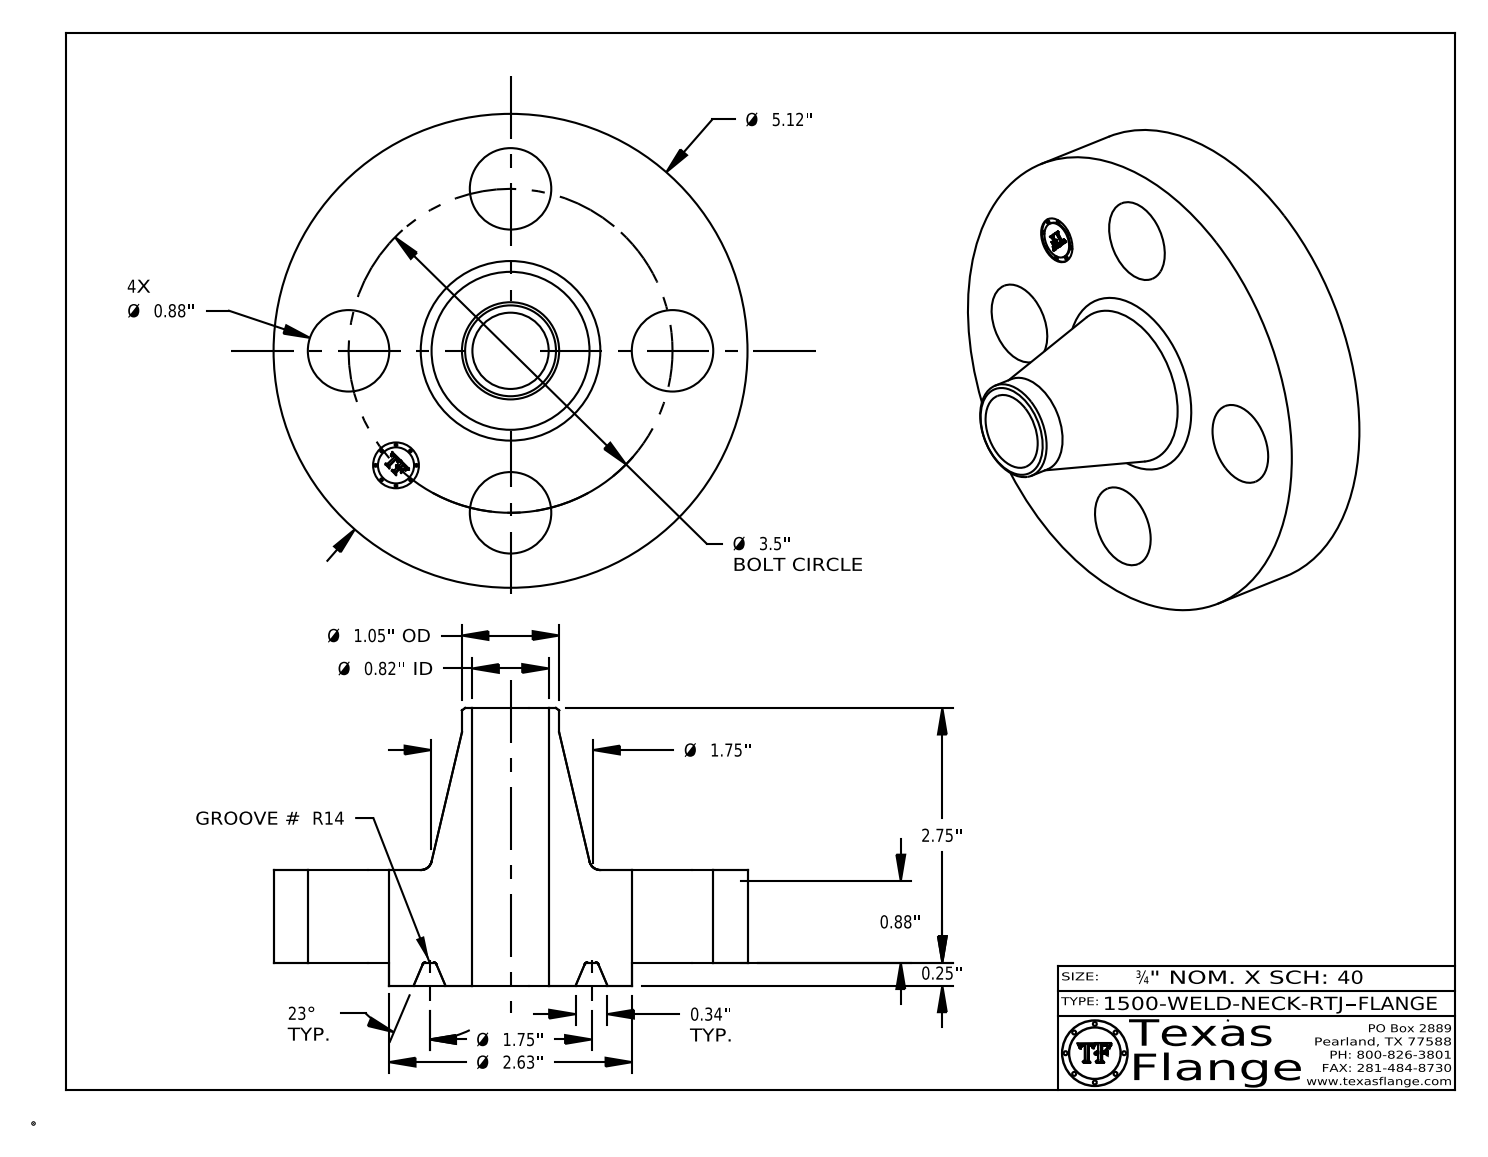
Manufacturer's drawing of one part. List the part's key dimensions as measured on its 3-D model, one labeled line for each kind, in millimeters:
Part name (STEP PRODUCT): 1500-WELD-NECK-RTJ
STEP written by: CATIA V5 STEP AP214 (AUTOMOTIVE_DESIGN)
Units: millimetres
Bodies: 1 solid, 425 faces (371 planar, 40 cylindrical, 14 other)
Overall size (bounding box): 130 × 130 × 76.2
Volume: 330 200 mm³ · Surface area: 51 550 mm²
Round holes (diameter × count): ⌀22.4 ×4, ⌀12.6 ×1, ⌀20.9 ×1
Round bosses / shafts (diameter × count): ⌀0.8 ×8, ⌀130 ×1, ⌀66.7 ×1, ⌀26.7 ×1, ⌀9.9 ×1
Main face-to-face distances: 25.4, 6.4, 31.8, 76.2, 69.9, 44.5, 0.4, 31.4, 25, 44.8
Hole centre spacings: 44.5, 62.9, 34, 82.1, 88.9
